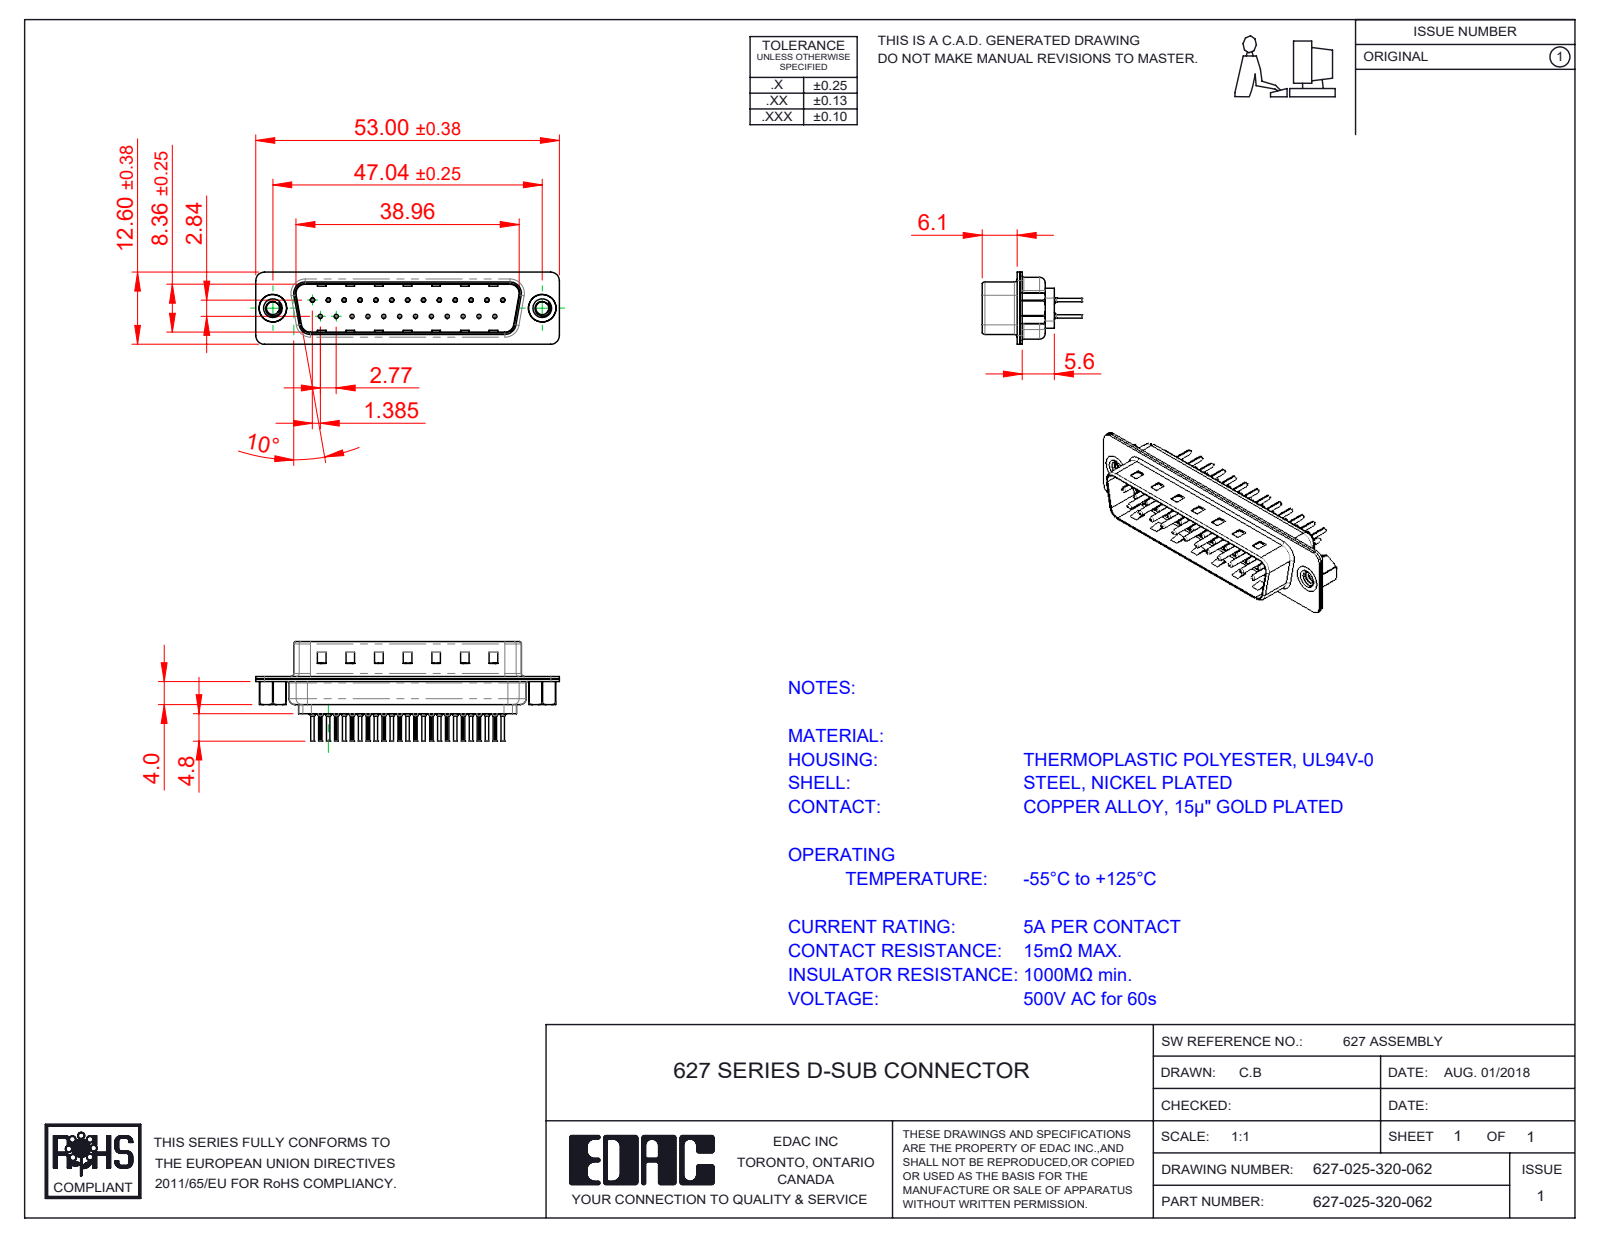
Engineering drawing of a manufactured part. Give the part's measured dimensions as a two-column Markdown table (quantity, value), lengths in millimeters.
| quantity | value |
| --- | --- |
| part name | 627-025-320-062; 627 Shell Front_25 Contacts; 627 Contact Row 2_20L; 627 4-40 Threaded Rivet (+3 more) |
| STEP written by | SolidWorks 2020 (CONFIG_CONTROL_DESIGN) |
| units | millimeters |
| bodies | 30 solids, 2822 faces (771 planar, 1060 cylindrical, 991 other) |
| overall size | 53 × 17.3 × 12.6 |
| volume | 2 677 mm³ |
| surface area | 7 794 mm² |
| round holes (diameter × count) | 0.2 × 25, 0.35 × 25, 1.1 × 25, 1.6 × 25, 2.26 × 2, 4 × 2, 4.8 × 2 |
| round bosses / shafts (diameter × count) | 2 × 25, 1.5 × 25, 0.75 × 25, 0.6 × 25, 5 × 2, 4.9 × 2 |
| partial cylindrical surfaces (radius × count) | 0.1 × 50, 1.5 × 16, 2 × 12, 0.5 × 8, 1.6 × 8, 0.25 × 4, 0.6 × 4, 0.65 × 4 |
| main face-to-face distances | 0.4, 0.45, 0.82, 9.58, 8.76, 0.9, 1.5, 1.4, 6.5, 6.05 |
| hole center spacings | 3.16, 8.31, 2.77, 5.54, 11.08, 16.62, 5.03, 5.04 |
